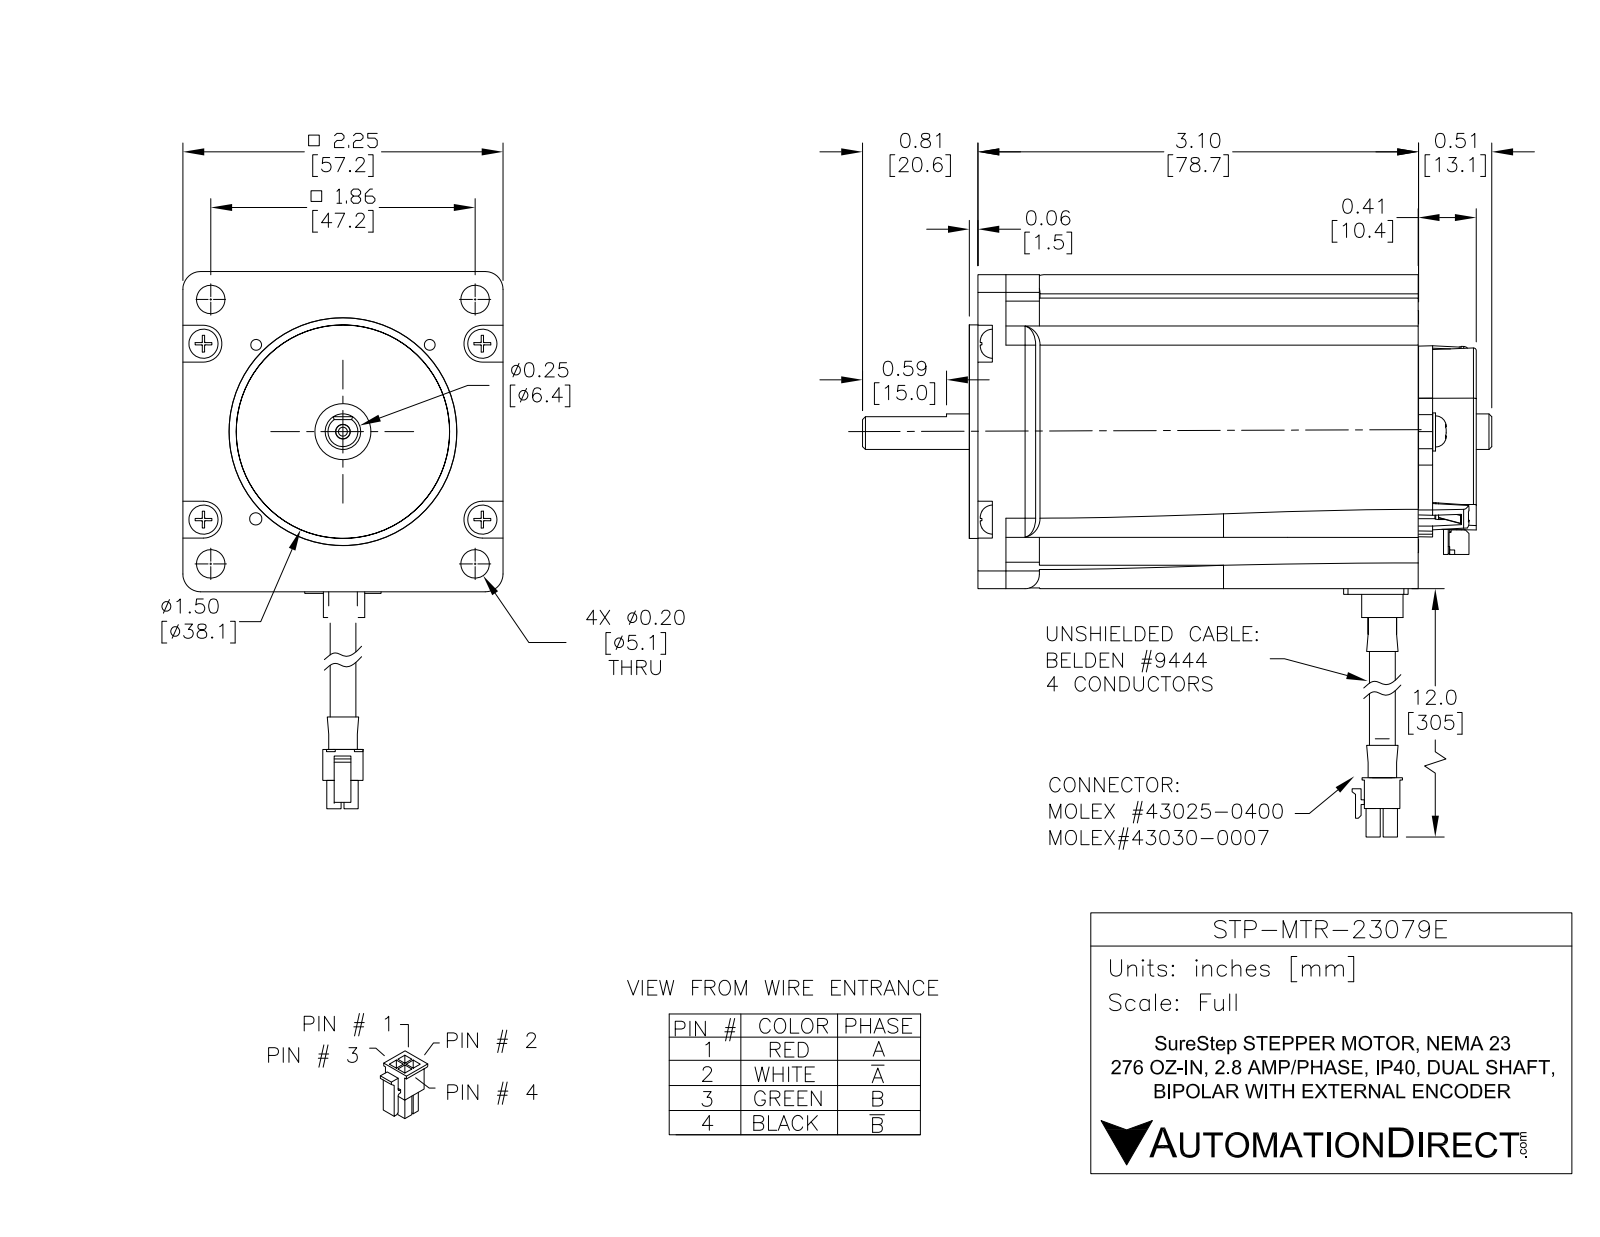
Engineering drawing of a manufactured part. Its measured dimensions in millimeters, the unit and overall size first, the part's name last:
Units: millimetres
Overall size (bounding box): 368.9 × 112.3 × 56.1
Round holes (diameter × count): ⌀0.8 ×4, ⌀0.9 ×4, ⌀2 ×4, ⌀2.5 ×4, ⌀3 ×4, ⌀5.1 ×4, ⌀1.7 ×2, ⌀2.2 ×2, ⌀2.3 ×2, ⌀2.9 ×2, ⌀3.2 ×2, ⌀3.2 ×2
Round bosses / shafts (diameter × count): ⌀1.5 ×4, ⌀6.8 ×2, ⌀43.2 ×1, ⌀38.1 ×1, ⌀11.8 ×1, ⌀10.5 ×1, ⌀7.4 ×1, ⌀5.5 ×1
Partial cylindrical surfaces — rounded edges, fillets, slot ends (radius × count): R0.3 ×24, R1 ×22, R3.2 ×10, R0.5 ×6, R1 ×6, R2 ×6, R0.3 ×4, R0.4 ×4
Main face-to-face distances: 56.1, 8, 27.5, 35.5, 78.7, 51.2, 43.2, 27.5, 35.4, 78.6
Hole centre spacings: 15.8, 49.1, 8, 18, 22, 29.4, 30, 33.4
Volume: 217 300 mm³ · Surface area: 49 380 mm²
Bodies: 12 solids, 2014 faces (1158 planar, 506 cylindrical, 350 other)
Part name (STEP PRODUCT): STP-MTR-23079E
STEP written by: SolidWorks 2017 (AUTOMOTIVE_DESIGN)
